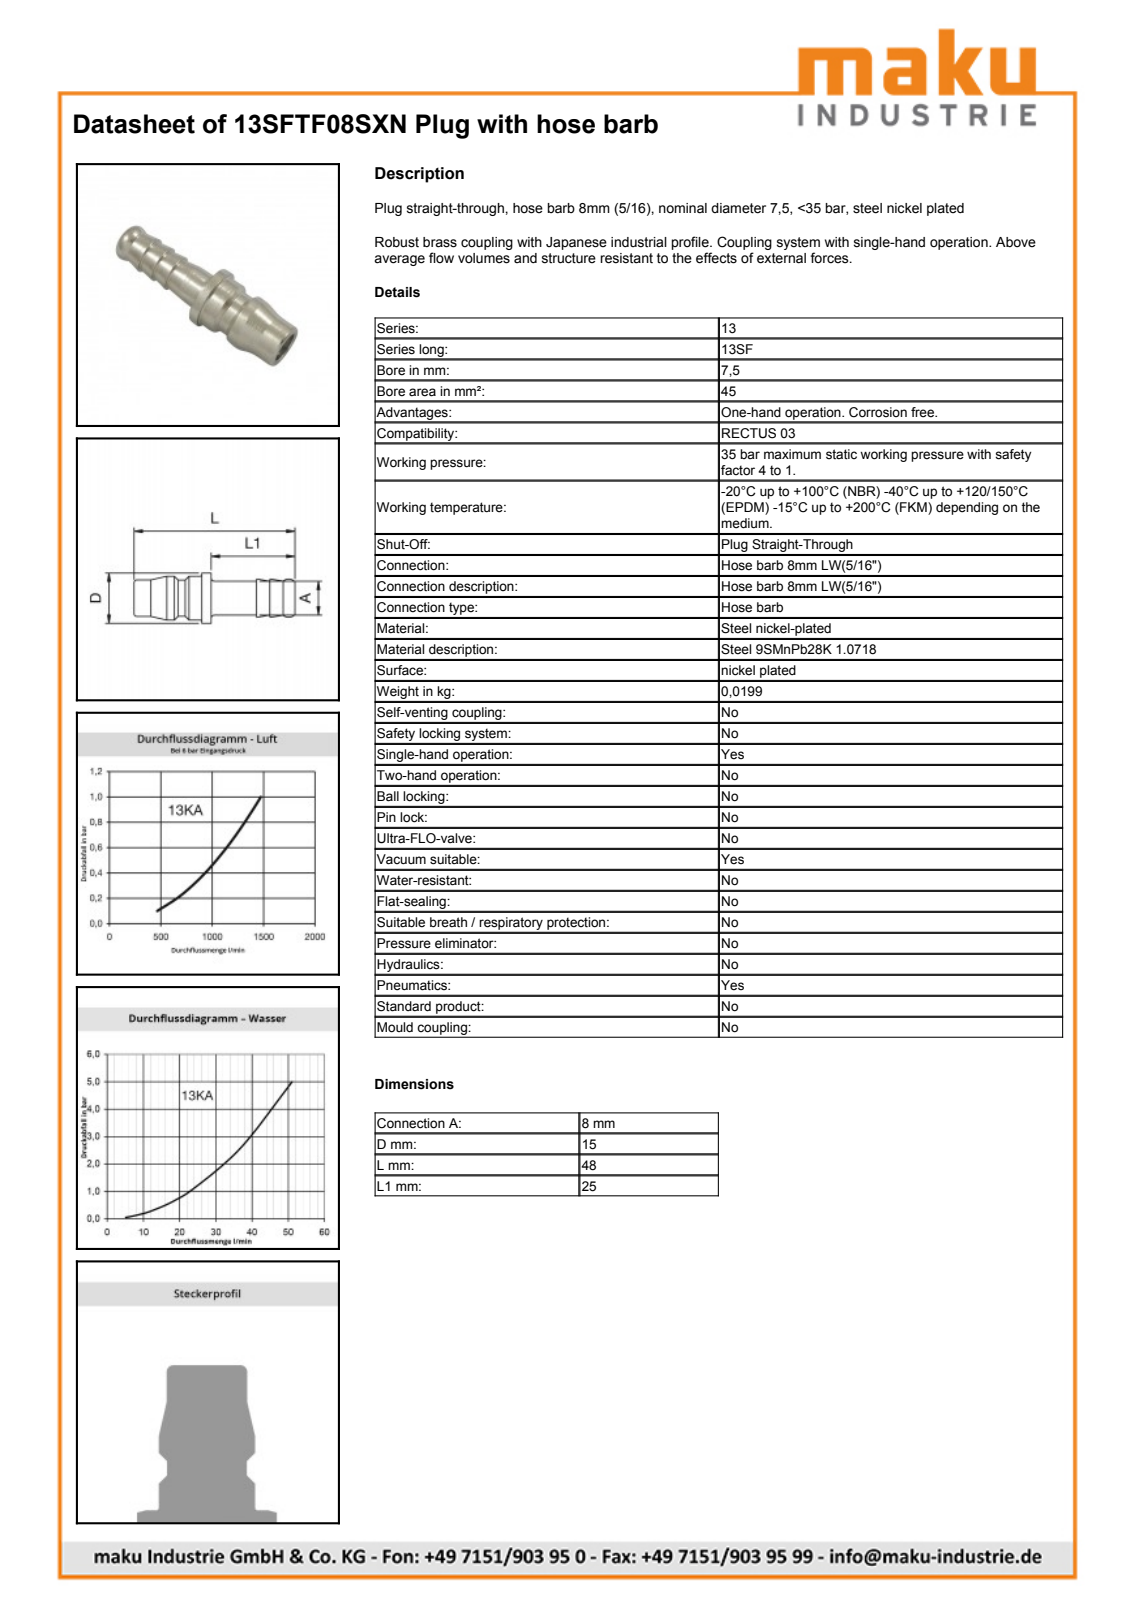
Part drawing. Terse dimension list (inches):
name: D104875
written by: Autodesk Inventor 2011 (AUTOMOTIVE_DESIGN)
unit: in
bodies: 1 solid, 28 faces (5 planar, 8 cylindrical, 15 other)
size: 1.89 × 0.591 × 0.591
volume: 0.152 in³; area: 4.379 in²
holes: 1× ⌀0.236, 1× ⌀0.295
bosses: 1× ⌀0.591, 1× ⌀0.516, 1× ⌀0.429, 1× ⌀0.425, 1× ⌀0.319
face distances: 0.906, 0.984, 1.89, 0.453, 0.531, 1.437, 1.094, 0.642, 0.11, 0.795
